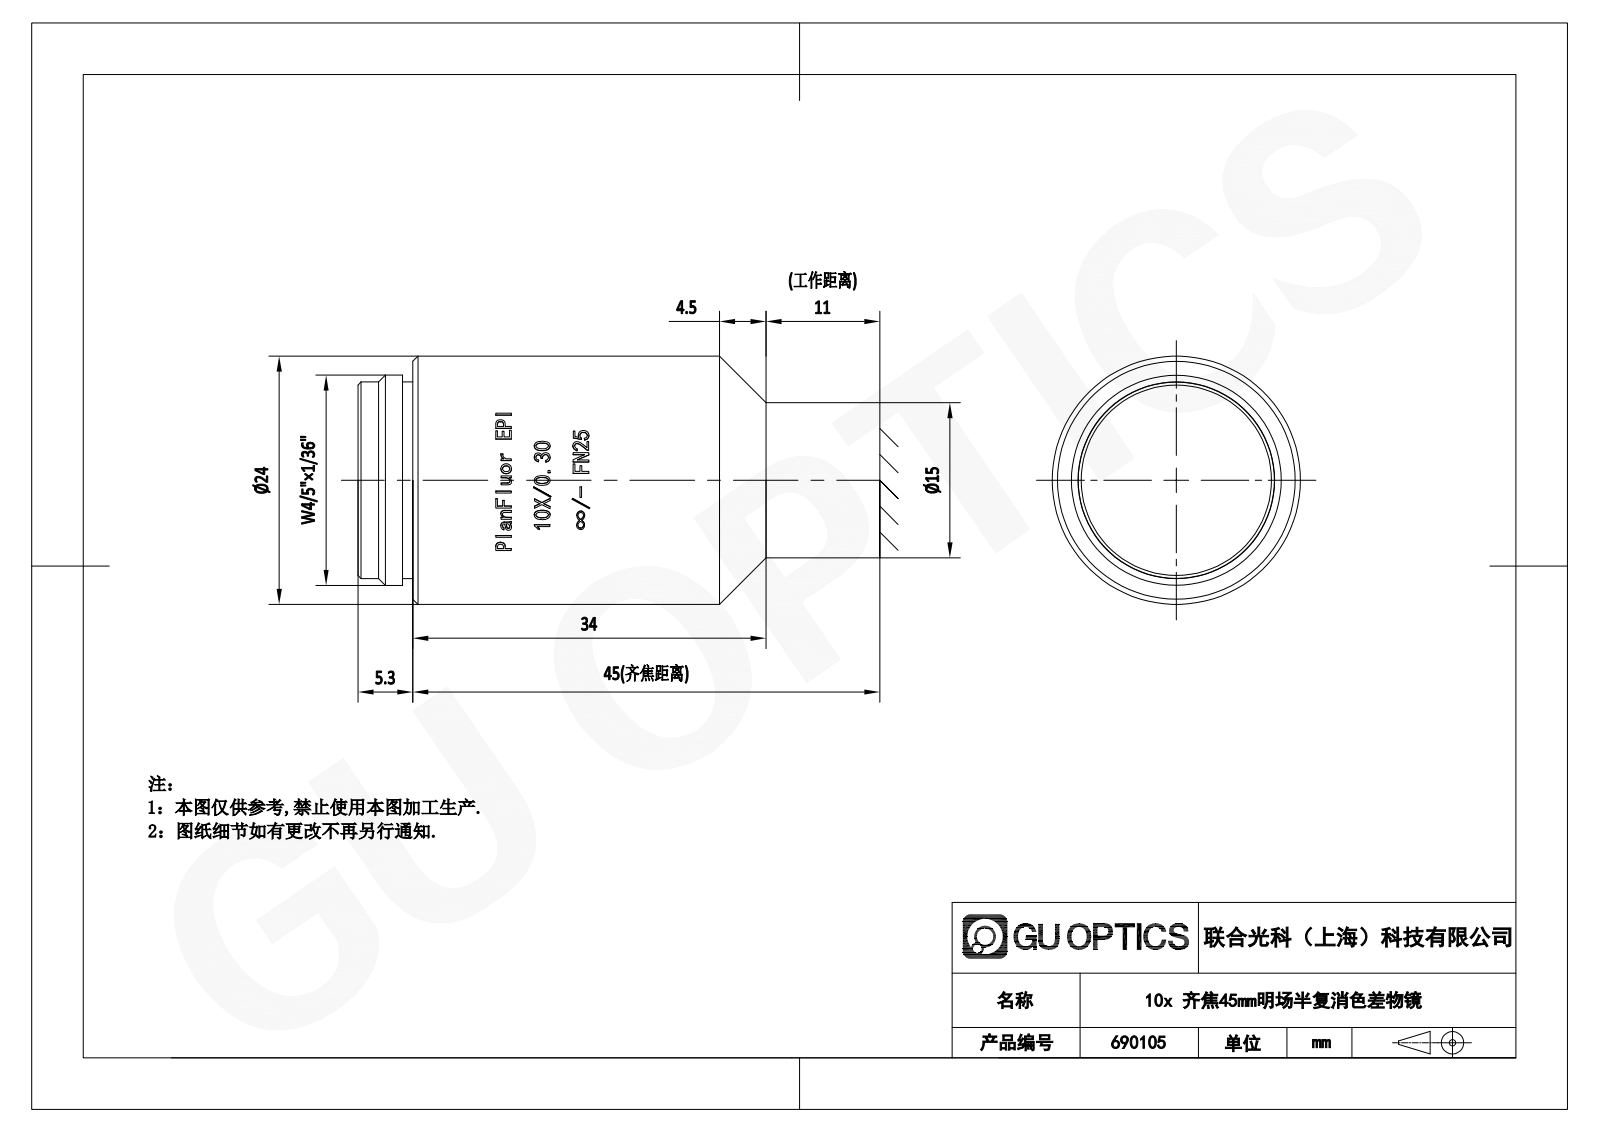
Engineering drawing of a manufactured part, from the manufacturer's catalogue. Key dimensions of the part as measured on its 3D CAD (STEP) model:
Part name (STEP PRODUCT): 690105
STEP written by: SolidWorks 2020 (CONFIG_CONTROL_DESIGN)
Units: millimetres
Bodies: 1 solid, 293 faces (130 planar, 44 cylindrical, 119 other)
Overall size (bounding box): 39.45 × 24.05 × 24
Volume: 16 352 mm³ · Surface area: 3 611 mm²
Round bosses / shafts (diameter × count): ⌀24 ×1, ⌀20.32 ×1, ⌀19 ×1
Partial cylindrical surfaces — rounded edges, fillets, slot ends (radius × count): R12.05 ×1
Main face-to-face distances: 39.45, 5.3, 34.15, 4.3, 1, 35.15, 2, 2.3, 3.3, 37.45
